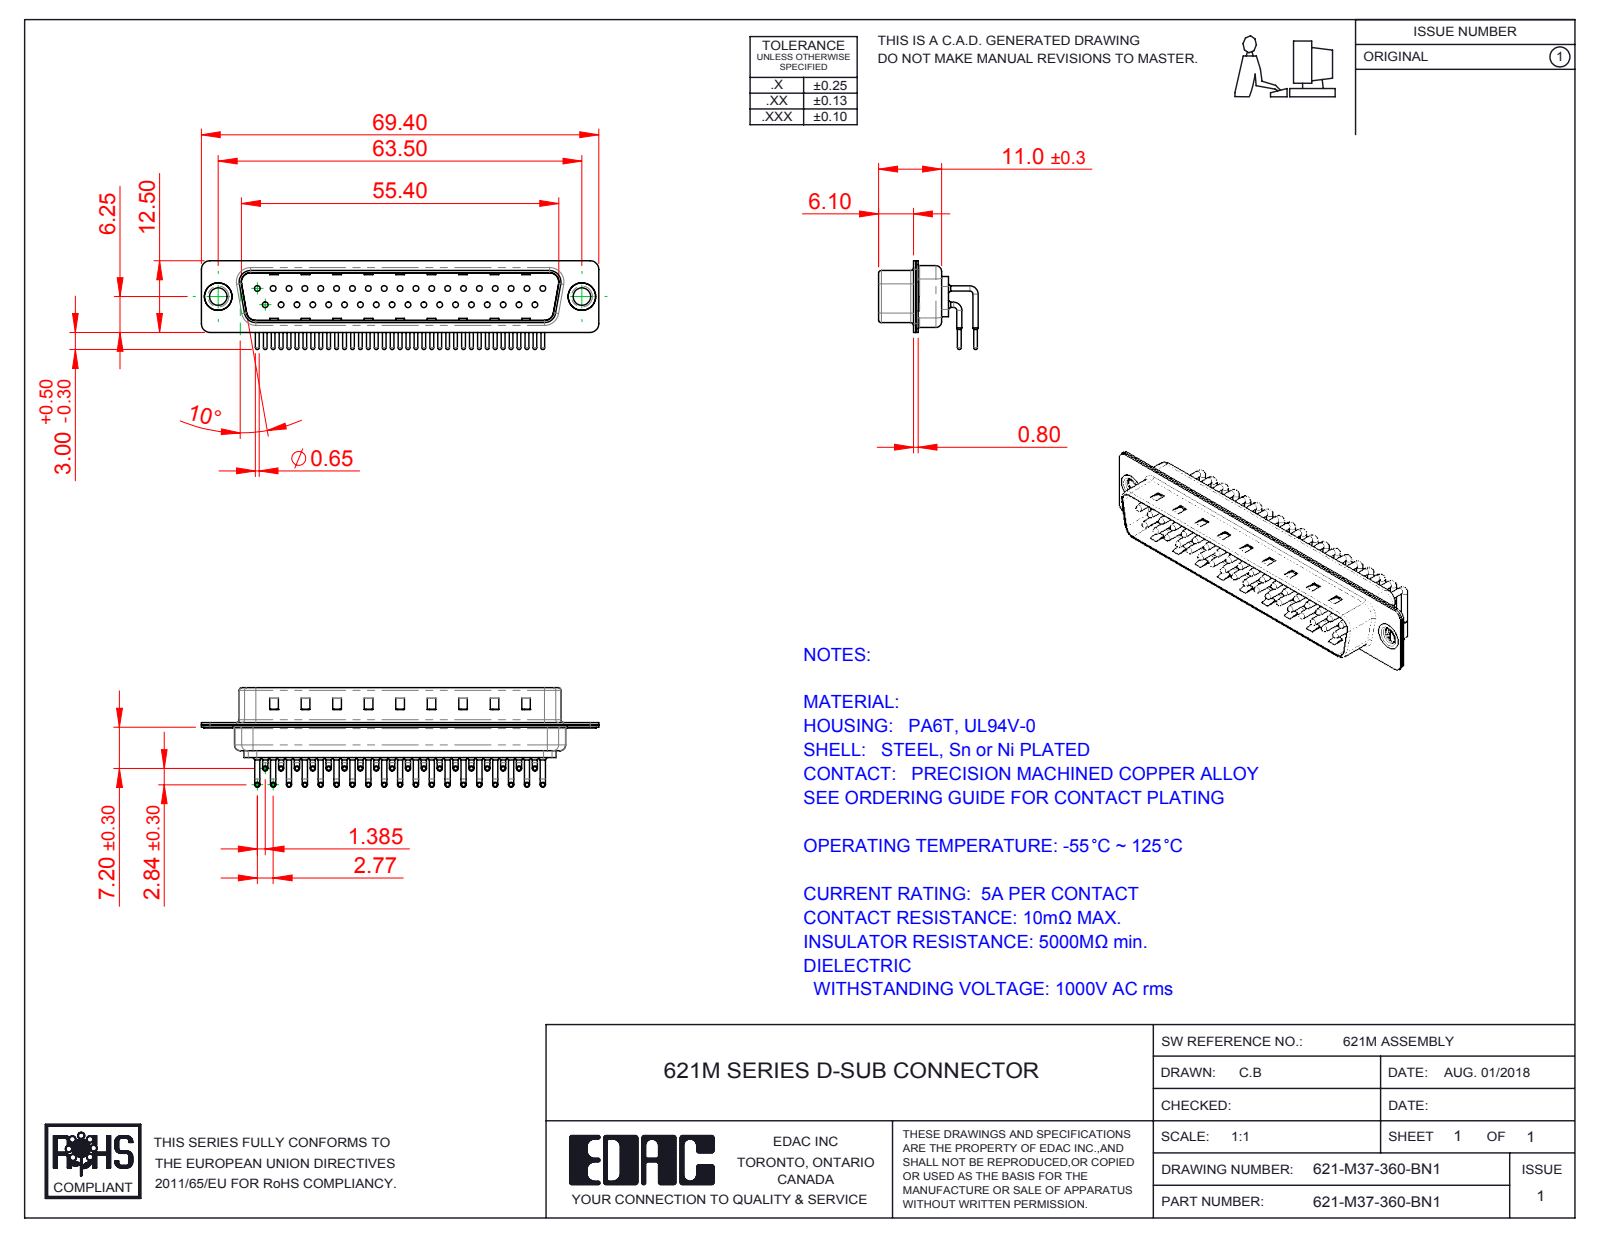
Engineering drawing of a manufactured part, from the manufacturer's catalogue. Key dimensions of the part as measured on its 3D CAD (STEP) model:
Part name (STEP PRODUCT): 621-M37-360-BN1; 621M Shell Front_37 Contacts; 621M Contact Row 2; 621M Housing_37 Contacts (+3 more)
STEP written by: SolidWorks 2016 (CONFIG_CONTROL_DESIGN)
Units: millimetres
Bodies: 42 solids, 4456 faces (2571 planar, 1457 cylindrical, 428 other)
Overall size (bounding box): 69.4 × 17.39 × 15.49
Volume: 3 918 mm³ · Surface area: 10 217 mm²
Round holes (diameter × count): ⌀1 ×37, ⌀1.7 ×37, ⌀2 ×37, ⌀3.05 ×2, ⌀4 ×2, ⌀4.8 ×2
Round bosses / shafts (diameter × count): ⌀0.9 ×74, ⌀1.5 ×37, ⌀0.65 ×37, ⌀5 ×2, ⌀4.9 ×2, ⌀3.55 ×2
Partial cylindrical surfaces — rounded edges, fillets, slot ends (radius × count): R1.01 ×37, R1.5 ×16, R2 ×12, R0.5 ×8, R1.6 ×8, R0.25 ×4, R0.6 ×4, R0.65 ×4
Main face-to-face distances: 0.4, 0.85, 9.55, 8.7, 1.25, 10.4, 1.5, 1.9, 0.35, 9.95
Hole centre spacings: 3.16, 2.77, 5.54, 8.31, 5.04, 10.1, 11.08, 12.78
